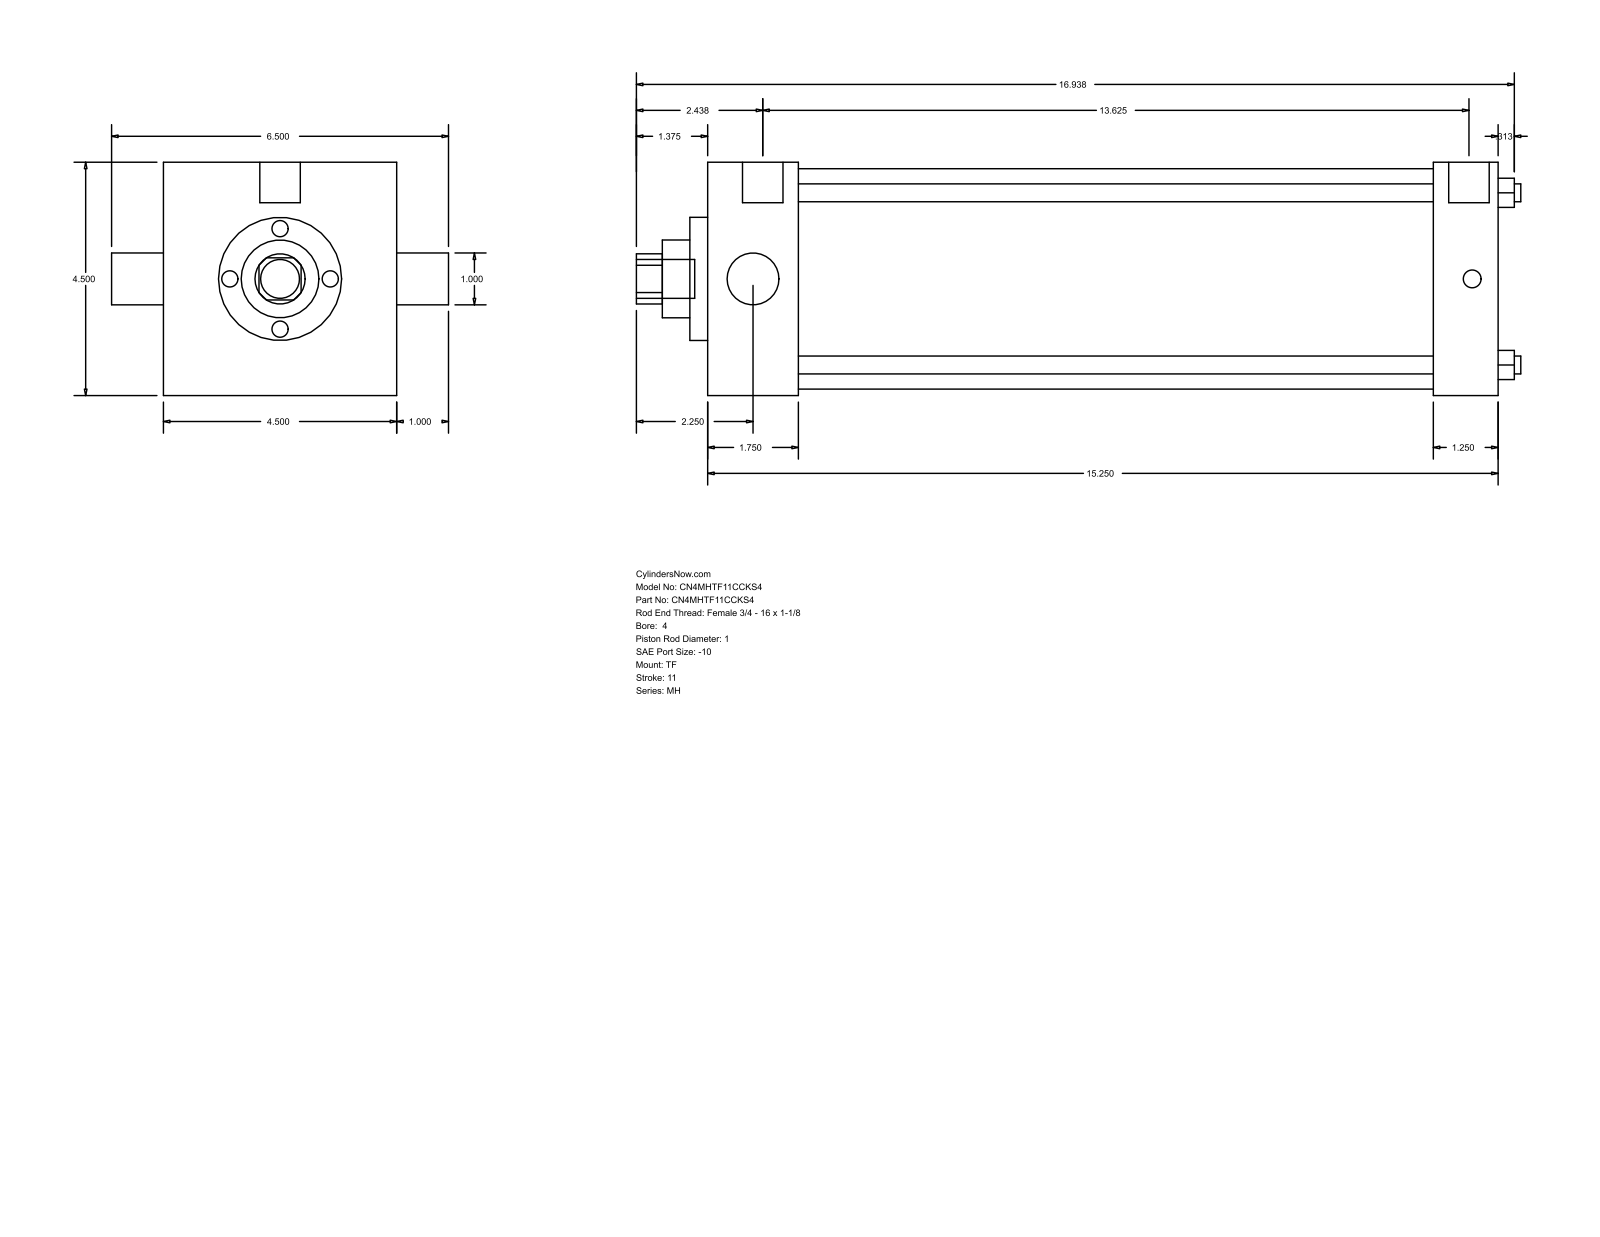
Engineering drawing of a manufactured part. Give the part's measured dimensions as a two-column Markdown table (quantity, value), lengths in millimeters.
| quantity | value |
| --- | --- |
| part name | MH_TF__0400_1 |
| STEP written by | GSSL Pune (CONFIG_CONTROL_DESIGN) |
| units | millimeters |
| bodies | 0 solids, 86 faces (61 planar, 25 cylindrical, 0 other) |
| overall size | 433.39 × 165.1 × 114.3 |
| round holes (diameter × count) | 8.76 × 4, 25.4 × 2, 38.1 × 1, 60.33 × 1, 107.95 × 1 |
| round bosses / shafts (diameter × count) | 8.73 × 3, 19.84 × 2, 19.05 × 1 |
| partial cylindrical surfaces (radius × count) | 12.29 × 1 |
| main face-to-face distances | 114.3, 387.35, 44.46, 342.89, 355.6, 311.14, 31.75, 8.73, 53.19, 364.33 |
| hole center spacings | 59.62, 84.32, 119.25 |
